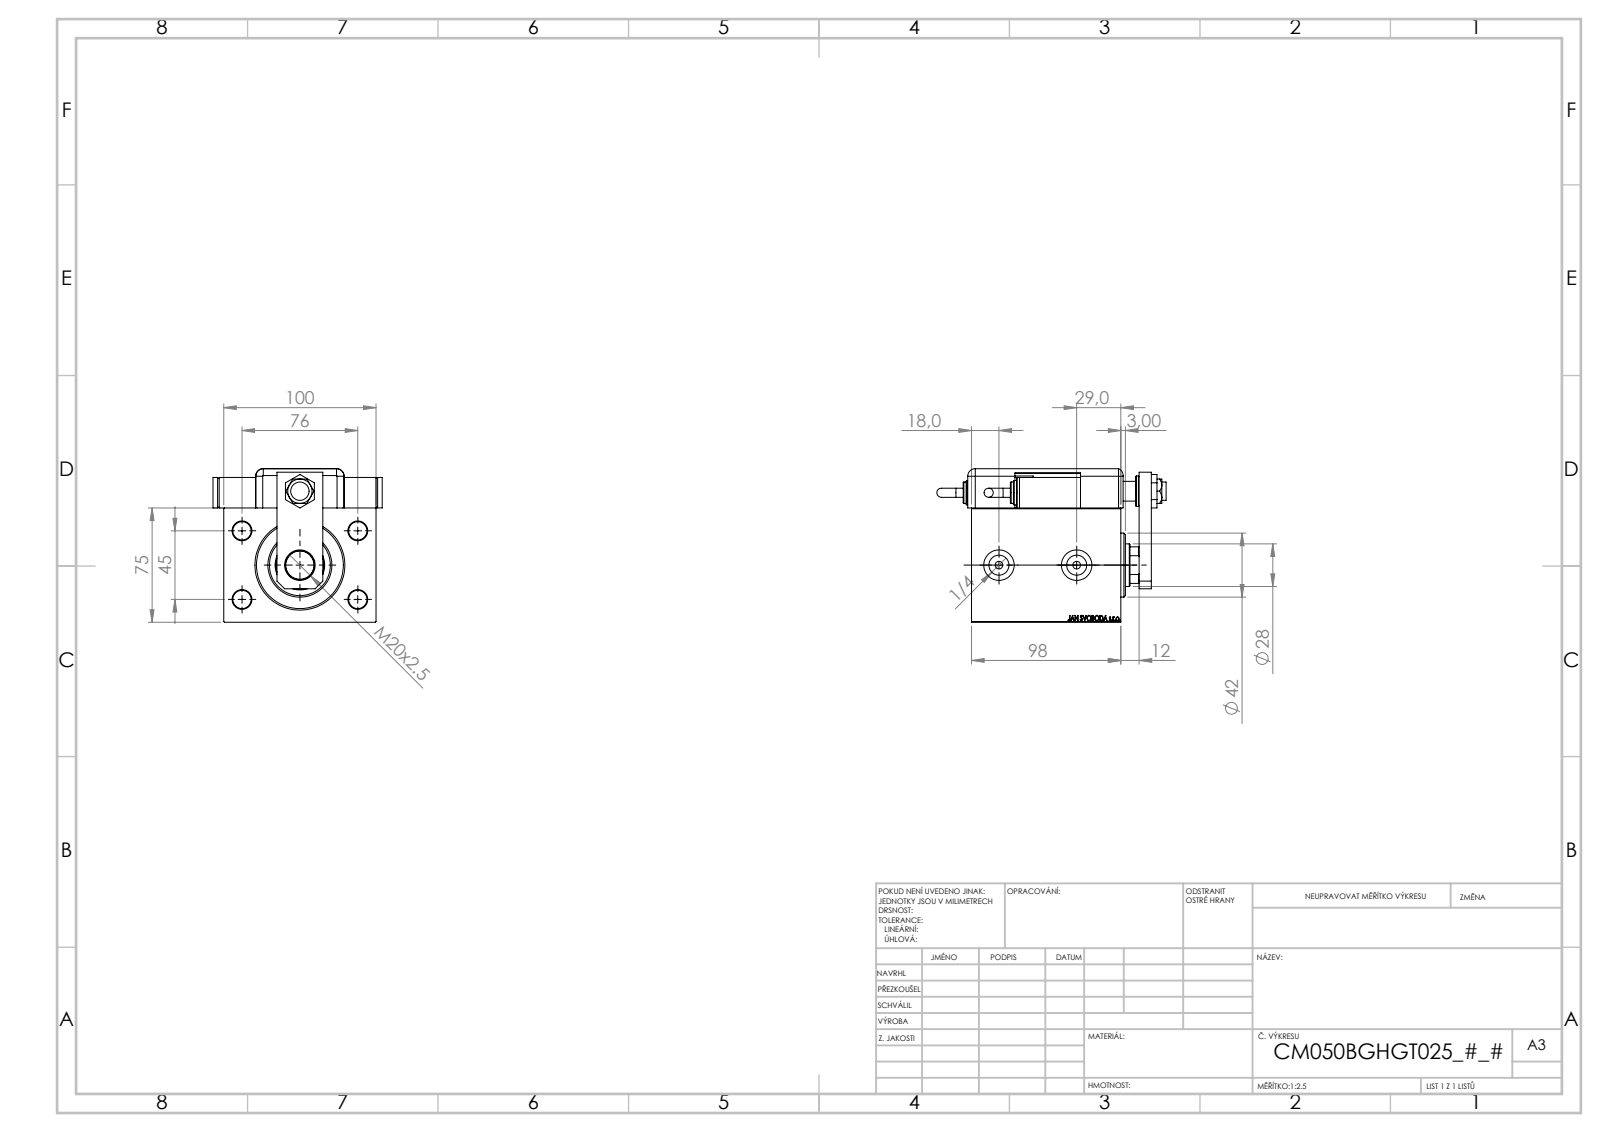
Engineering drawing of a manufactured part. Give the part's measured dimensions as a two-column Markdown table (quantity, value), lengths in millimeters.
| quantity | value |
| --- | --- |
| part name | NUT_D13; V450CM_B_Body; SWITCH DIM A_G; NUT_D19 (+7 more) |
| STEP written by | SolidWorks 2019 (CONFIG_CONTROL_DESIGN) |
| units | millimeters |
| bodies | 13 solids, 1268 faces (608 planar, 111 cylindrical, 549 other) |
| overall size | 150.46 × 111 × 100.8 |
| volume | 821 065 mm³ |
| surface area | 148 913 mm² |
| round holes (diameter × count) | 12 × 5, 20 × 3, 4 × 2, 5 × 2, 8 × 2, 13.16 × 2, 13 × 1, 14 × 1, 18.5 × 1, 28 × 1, 31.5 × 1, 32.5 × 1 |
| round bosses / shafts (diameter × count) | 20 × 3, 16 × 2, 14 × 2, 6 × 2, 42 × 1 |
| partial cylindrical surfaces (radius × count) | 5 × 9, 10 × 1, 13.5 × 1 |
| main face-to-face distances | 75, 3, 98, 100, 14, 20, 84, 25.8, 100.8, 13.5 |
| hole center spacings | 44.16, 45, 46.04, 76, 80.53, 88.32, 20, 48.5 |
